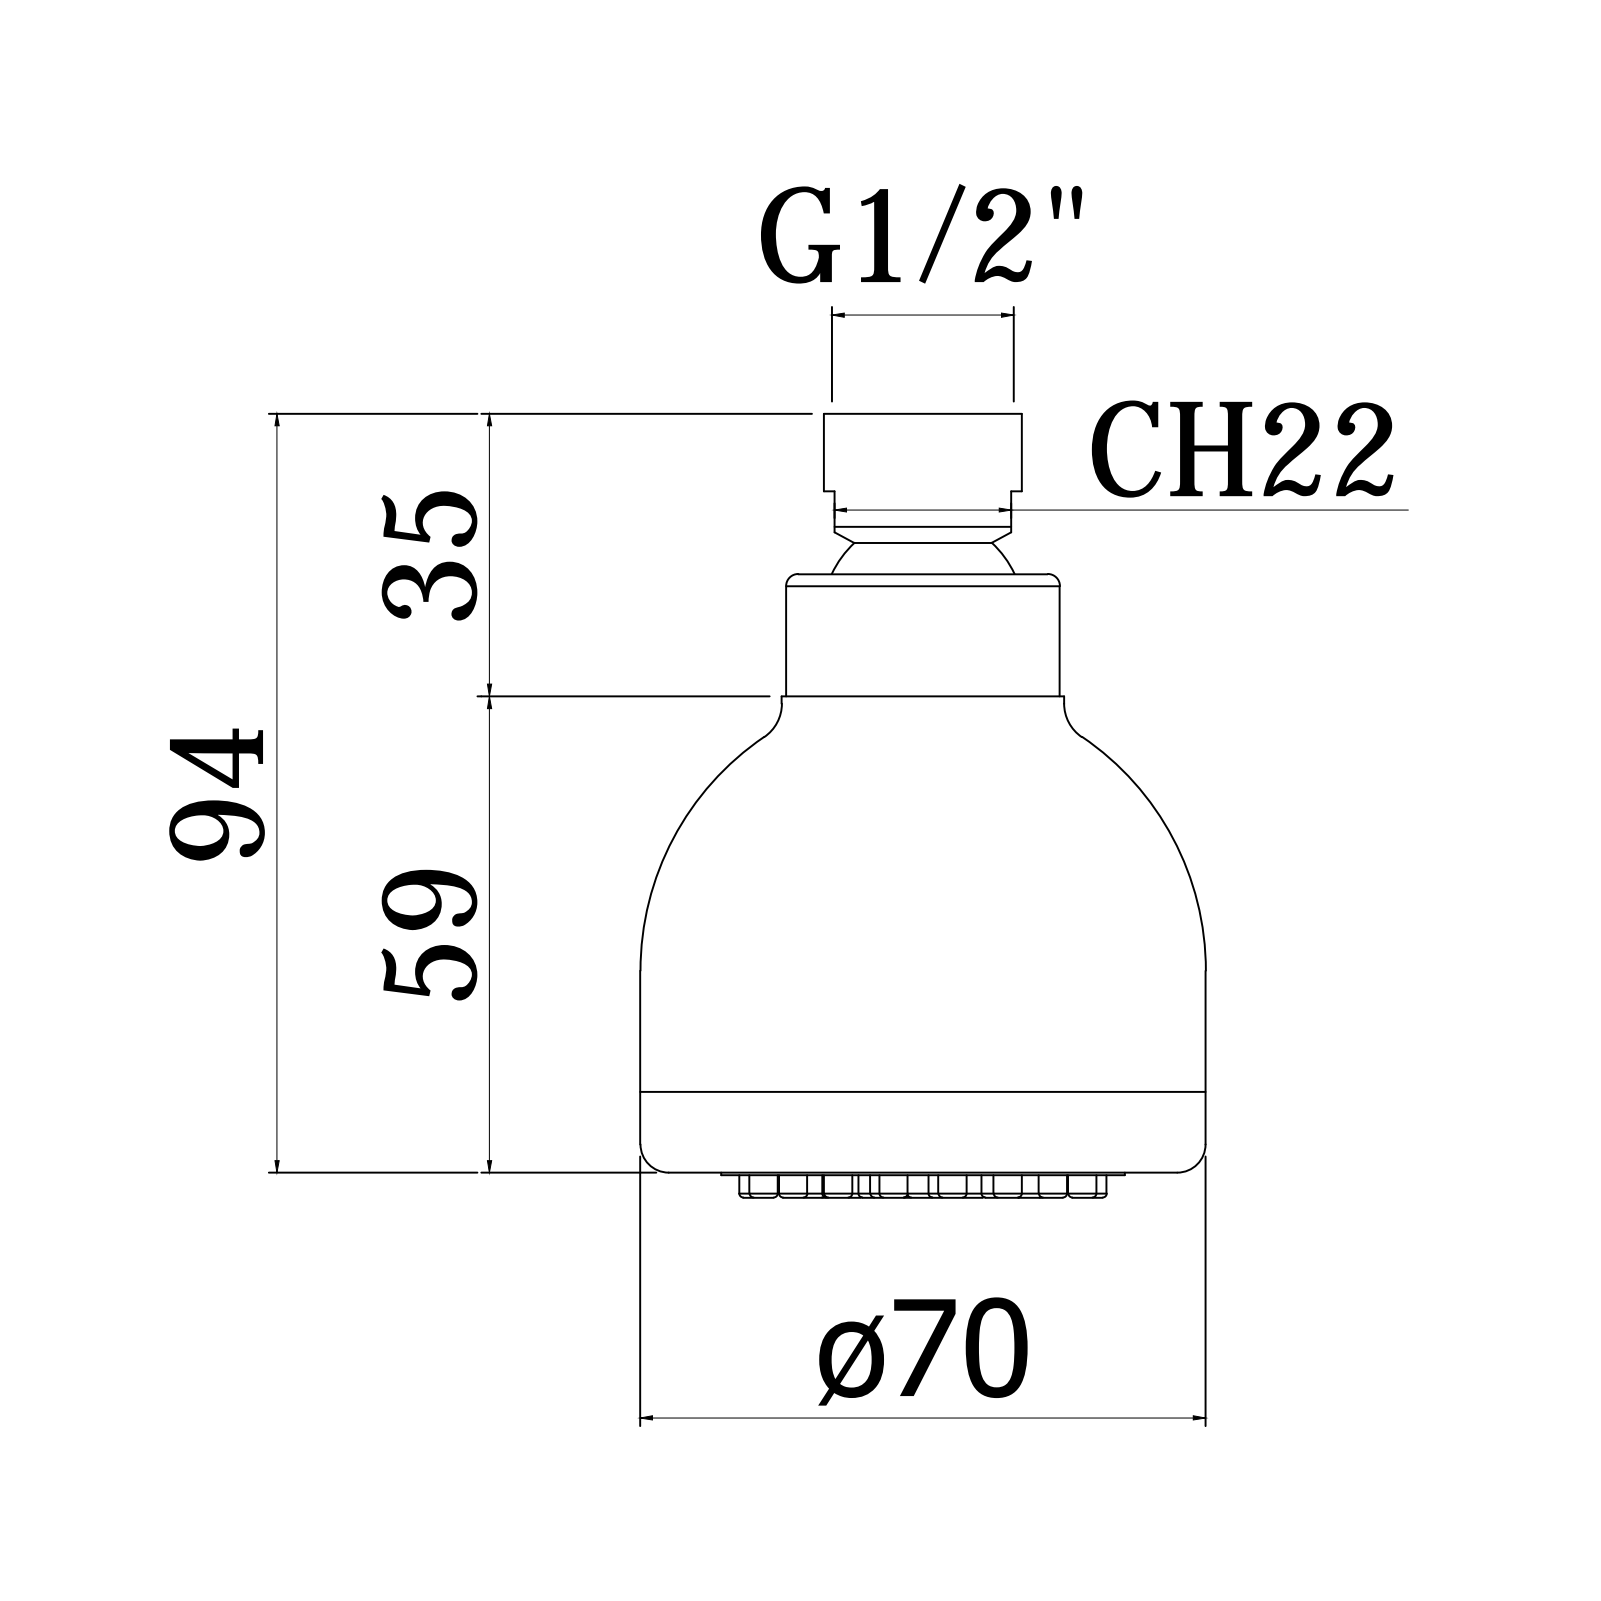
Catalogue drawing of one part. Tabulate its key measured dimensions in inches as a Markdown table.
| quantity | value |
| --- | --- |
| part name | 4071304CR |
| STEP written by | CREO PARAMETRIC BY PTC INC, 2020044 (CONFIG_CONTROL_DESIGN) |
| units | inches |
| bodies | 1 solid, 5644 faces (3810 planar, 1064 cylindrical, 770 other) |
| overall size | 3.958 × 2.756 × 2.756 |
| volume | 5.235 in³ |
| surface area | 94.72 in² |
| round holes (diameter × count) | 0.181 × 10, 0.134 × 1, 0.157 × 1, 0.197 × 1, 0.268 × 1, 0.48 × 1, 0.549 × 1, 0.733 × 1, 0.807 × 1, 0.825 × 1, 0.961 × 1, 1.008 × 1 |
| round bosses / shafts (diameter × count) | 2.756 × 1, 1.398 × 1, 1.118 × 1, 1.102 × 1, 0.992 × 1, 0.984 × 1, 0.906 × 1, 0.744 × 1 |
| partial cylindrical surfaces (radius × count) | 0.173 × 18, 0.197 × 18, 0.039 × 6, 0.028 × 1, 0.077 × 1, 0.078 × 1, 0.079 × 1, 0.554 × 1 |
| main face-to-face distances | 0.047, 0.177, 1.674, 0.197, 2.541, 2.737, 0.02, 2.363, 0.866, 0.689 |
| hole center spacings | 0.299, 0.484, 0.569, 0.783, 0.921, 0.969 |
